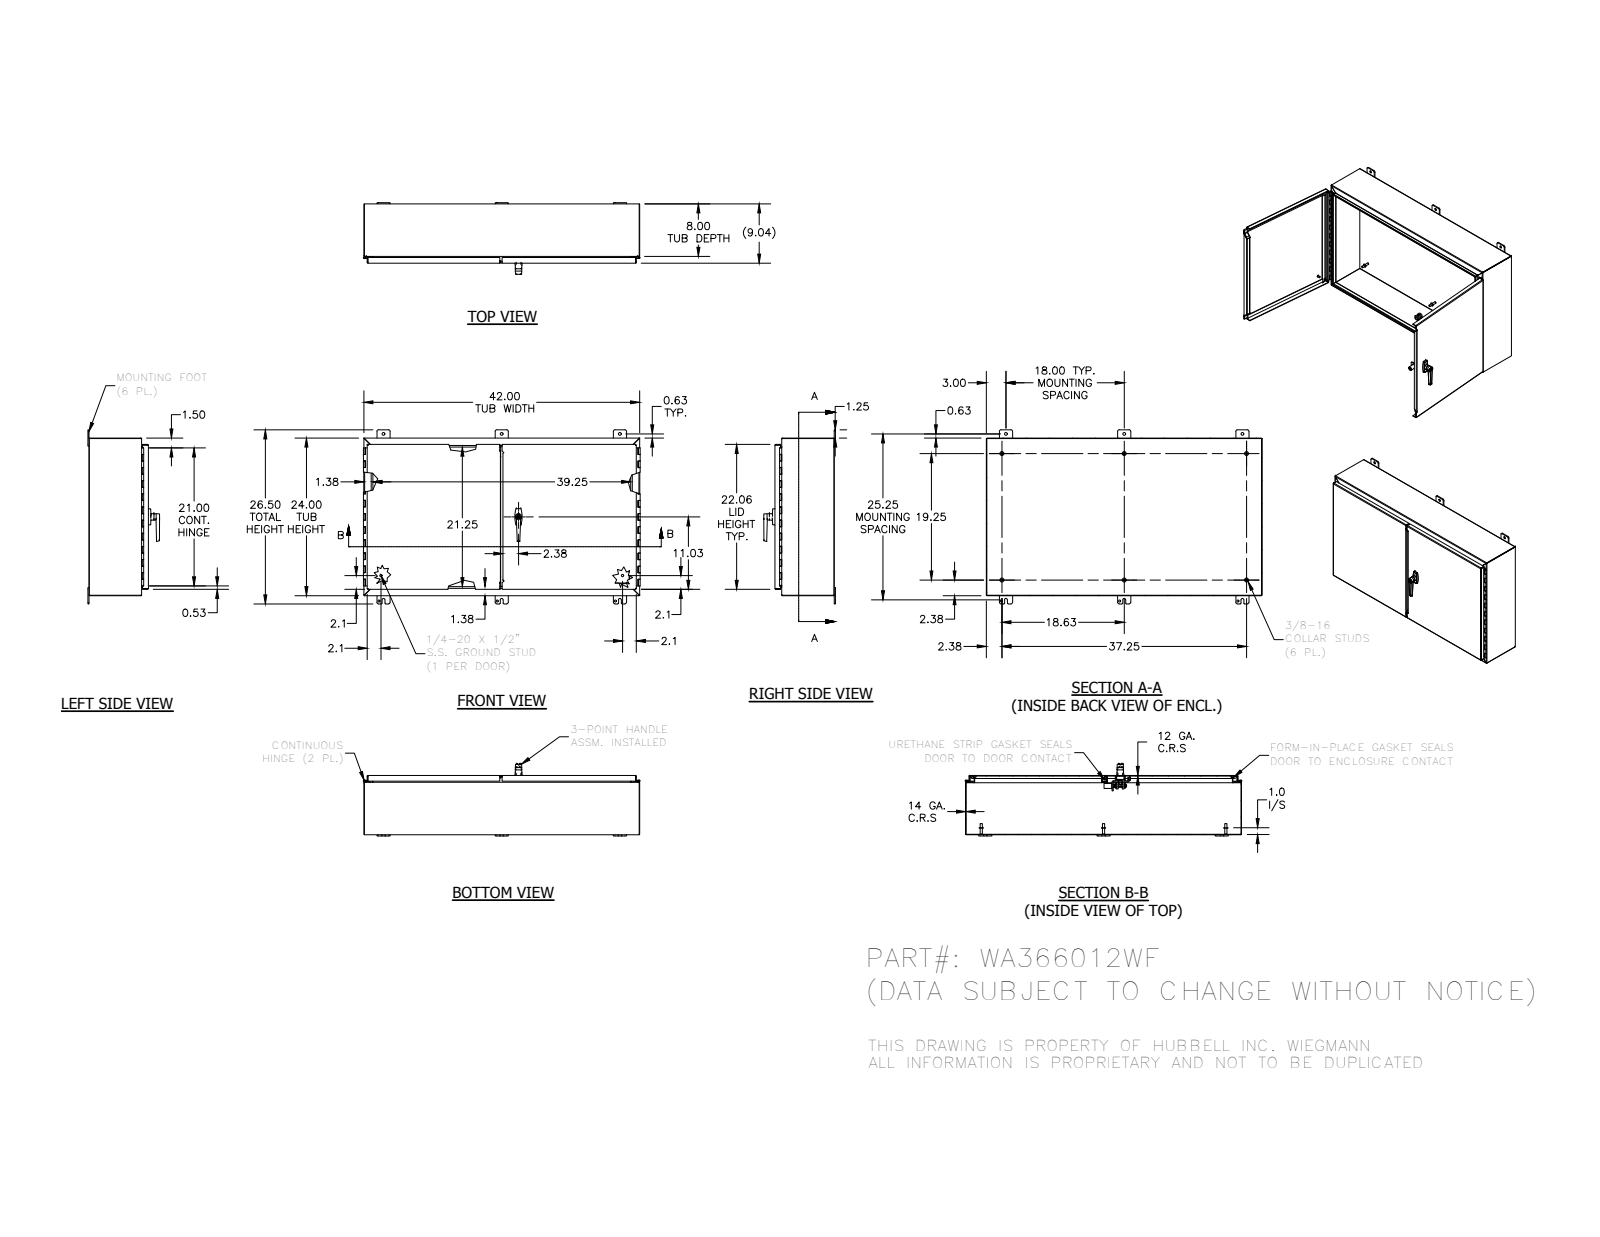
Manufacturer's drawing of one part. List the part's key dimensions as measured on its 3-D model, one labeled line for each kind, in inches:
Part name (STEP PRODUCT): WA244208WF; WA244208WFLRS; 34840; WA244208WFBTB (+8 more)
STEP written by: Autodesk Inventor 2012 (AUTOMOTIVE_DESIGN)
Units: inches
Bodies: 60 solids, 2452 faces (1334 planar, 628 cylindrical, 490 other)
Overall size (bounding box): 42.148 × 26.5 × 10.919
Volume: 327.2 in³ · Surface area: 7 594 in²
Round holes (diameter × count): ⌀0.277 ×8, ⌀0.083 ×6, ⌀0.313 ×6, ⌀0.438 ×6, ⌀0.2 ×4, ⌀0.125 ×2, ⌀0.159 ×2, ⌀0.241 ×2, ⌀0.25 ×2, ⌀0.252 ×2, ⌀0.4 ×2, ⌀0.407 ×2
Round bosses / shafts (diameter × count): ⌀0.157 ×7, ⌀0.625 ×6, ⌀0.33 ×6, ⌀0.25 ×4, ⌀0.115 ×4, ⌀1 ×2, ⌀0.563 ×2, ⌀0.527 ×2
Partial cylindrical surfaces — rounded edges, fillets, slot ends (radius × count): R0.031 ×28, R0.25 ×24, R0.008 ×22, R0.016 ×22, R0.105 ×17, R0.01 ×16, R0.05 ×14, R0.125 ×12
Main face-to-face distances: 0.074, 0.094, 8.942, 8.868, 9.035, 8.961, 23.926, 41.926, 24, 23.852
Hole centre spacings: 18, 0.293, 0.201, 17.372, 18.742, 30, 30, 36
